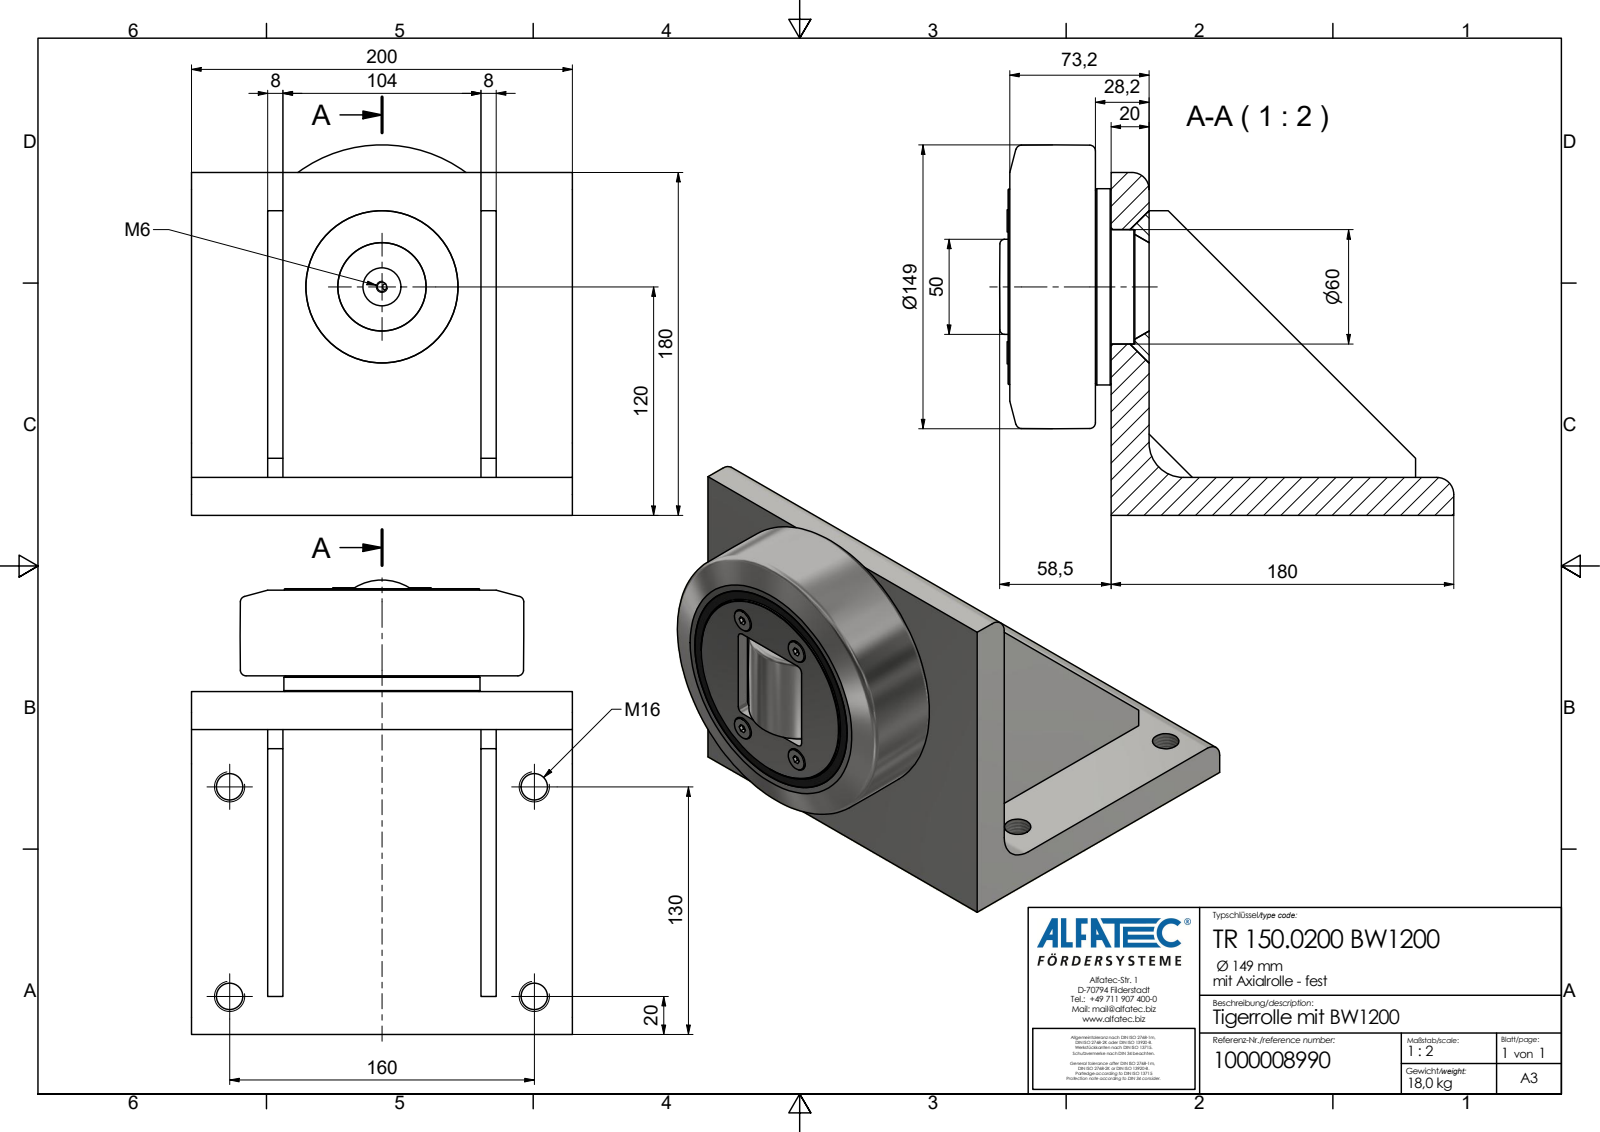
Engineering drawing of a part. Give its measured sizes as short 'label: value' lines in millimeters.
name: TR 150.0200 BW1200_Kontur
written by: Autodesk Inventor 2020 (AP242_MANAGED_MODEL_BASED_3D_ENGINEERING_MIM_LF)
unit: mm
bodies: 1 solid, 86 faces (58 planar, 14 cylindrical, 14 other)
size: 238.5 × 200 × 194.5
volume: 2 379 000 mm³; area: 241 009 mm²
holes: 4× ⌀13.84
bosses: 4× ⌀11.7, 1× ⌀103, 1× ⌀102.5, 1× ⌀101.4
rounds: 2× R9, 1× R18
face distances: 20, 8, 112, 160, 40, 48, 152, 104, 120, 8.2
hole spacings: 110, 160, 194.16
